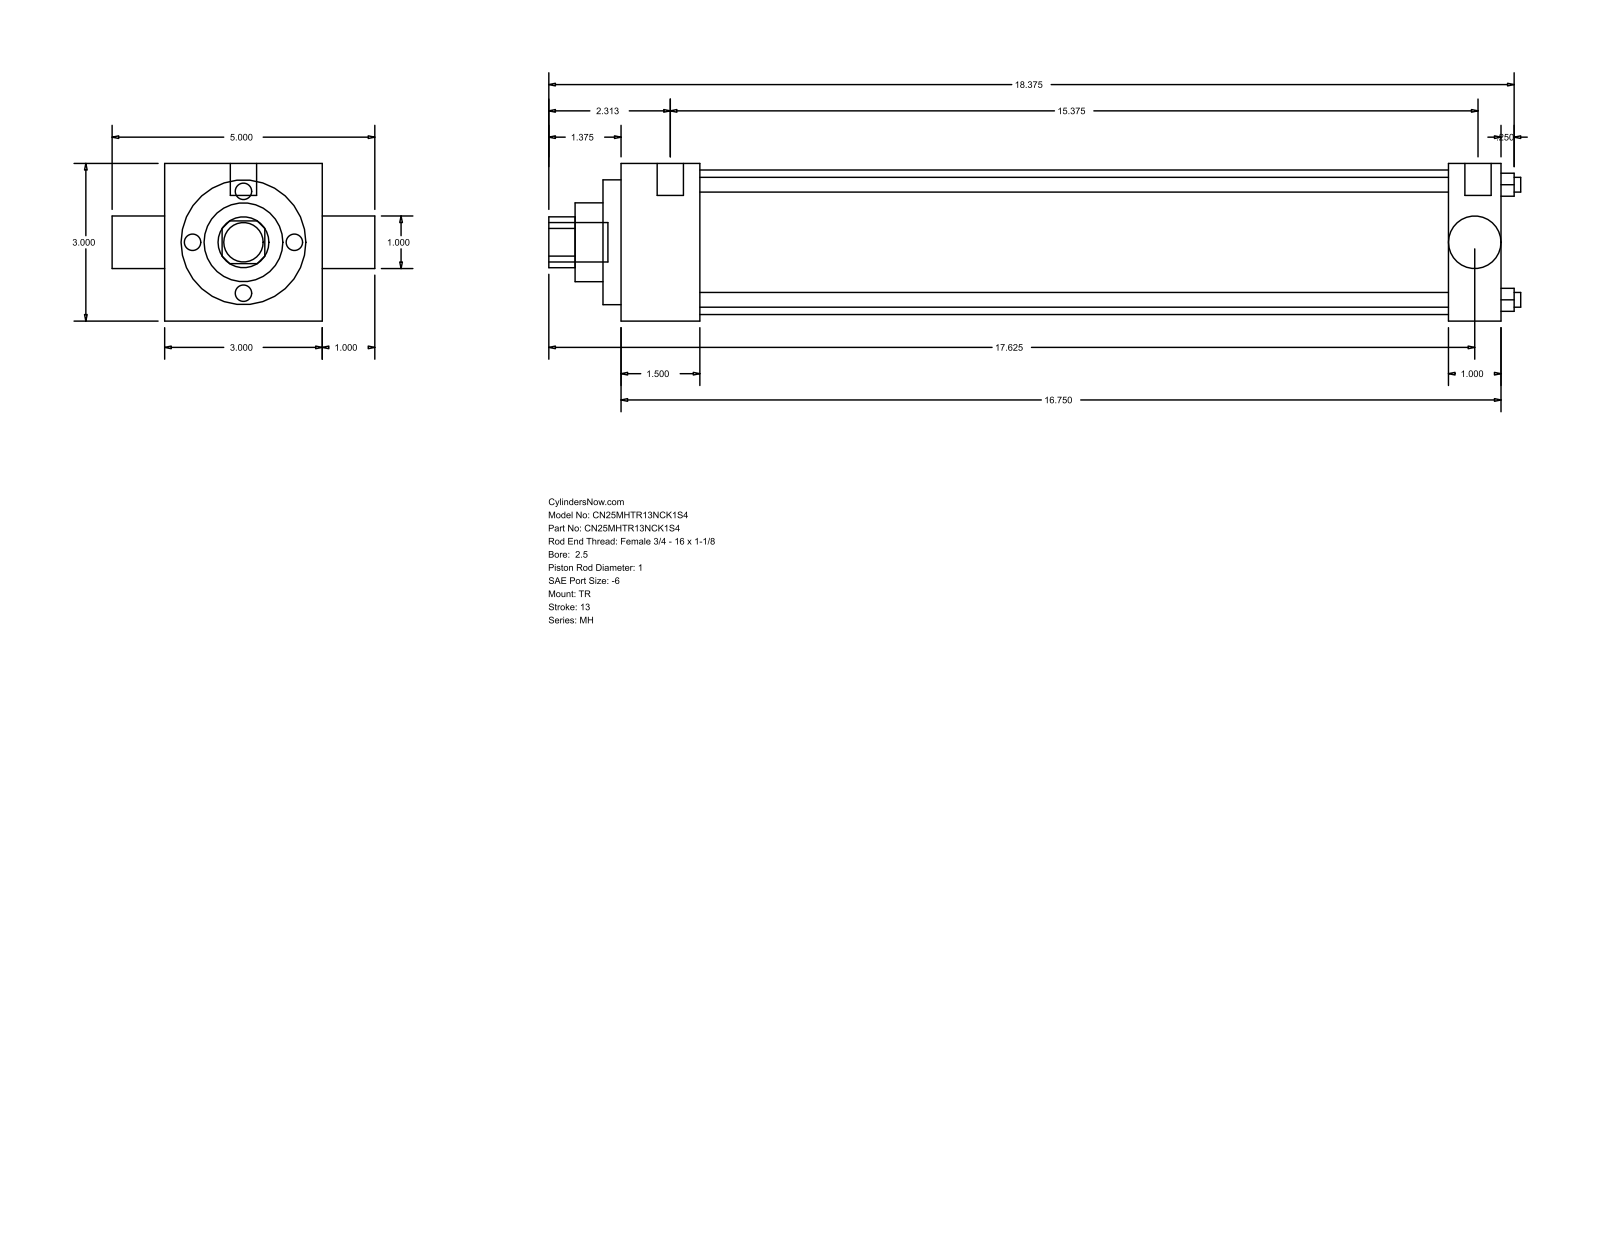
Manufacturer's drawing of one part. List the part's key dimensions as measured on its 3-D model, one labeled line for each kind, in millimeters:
Part name (STEP PRODUCT): MH_TR__0250_1
STEP written by: GSSL Pune (CONFIG_CONTROL_DESIGN)
Units: millimetres
Bodies: 0 solids, 86 faces (61 planar, 25 cylindrical, 0 other)
Overall size (bounding box): 469.9 × 127 × 76.2
Round holes (diameter × count): ⌀7.14 ×4, ⌀25.35 ×1, ⌀25.4 ×1, ⌀38.1 ×1, ⌀60.33 ×1, ⌀69.85 ×1
Round bosses / shafts (diameter × count): ⌀5.56 ×3, ⌀12.7 ×2, ⌀19.05 ×1
Partial cylindrical surfaces — rounded edges, fillets, slot ends (radius × count): R12.29 ×1
Main face-to-face distances: 76.2, 425.46, 25.4, 38.11, 387.35, 400.06, 361.95, 8.73, 46.84, 408.79
Hole centre spacings: 39.33, 55.62, 78.66
